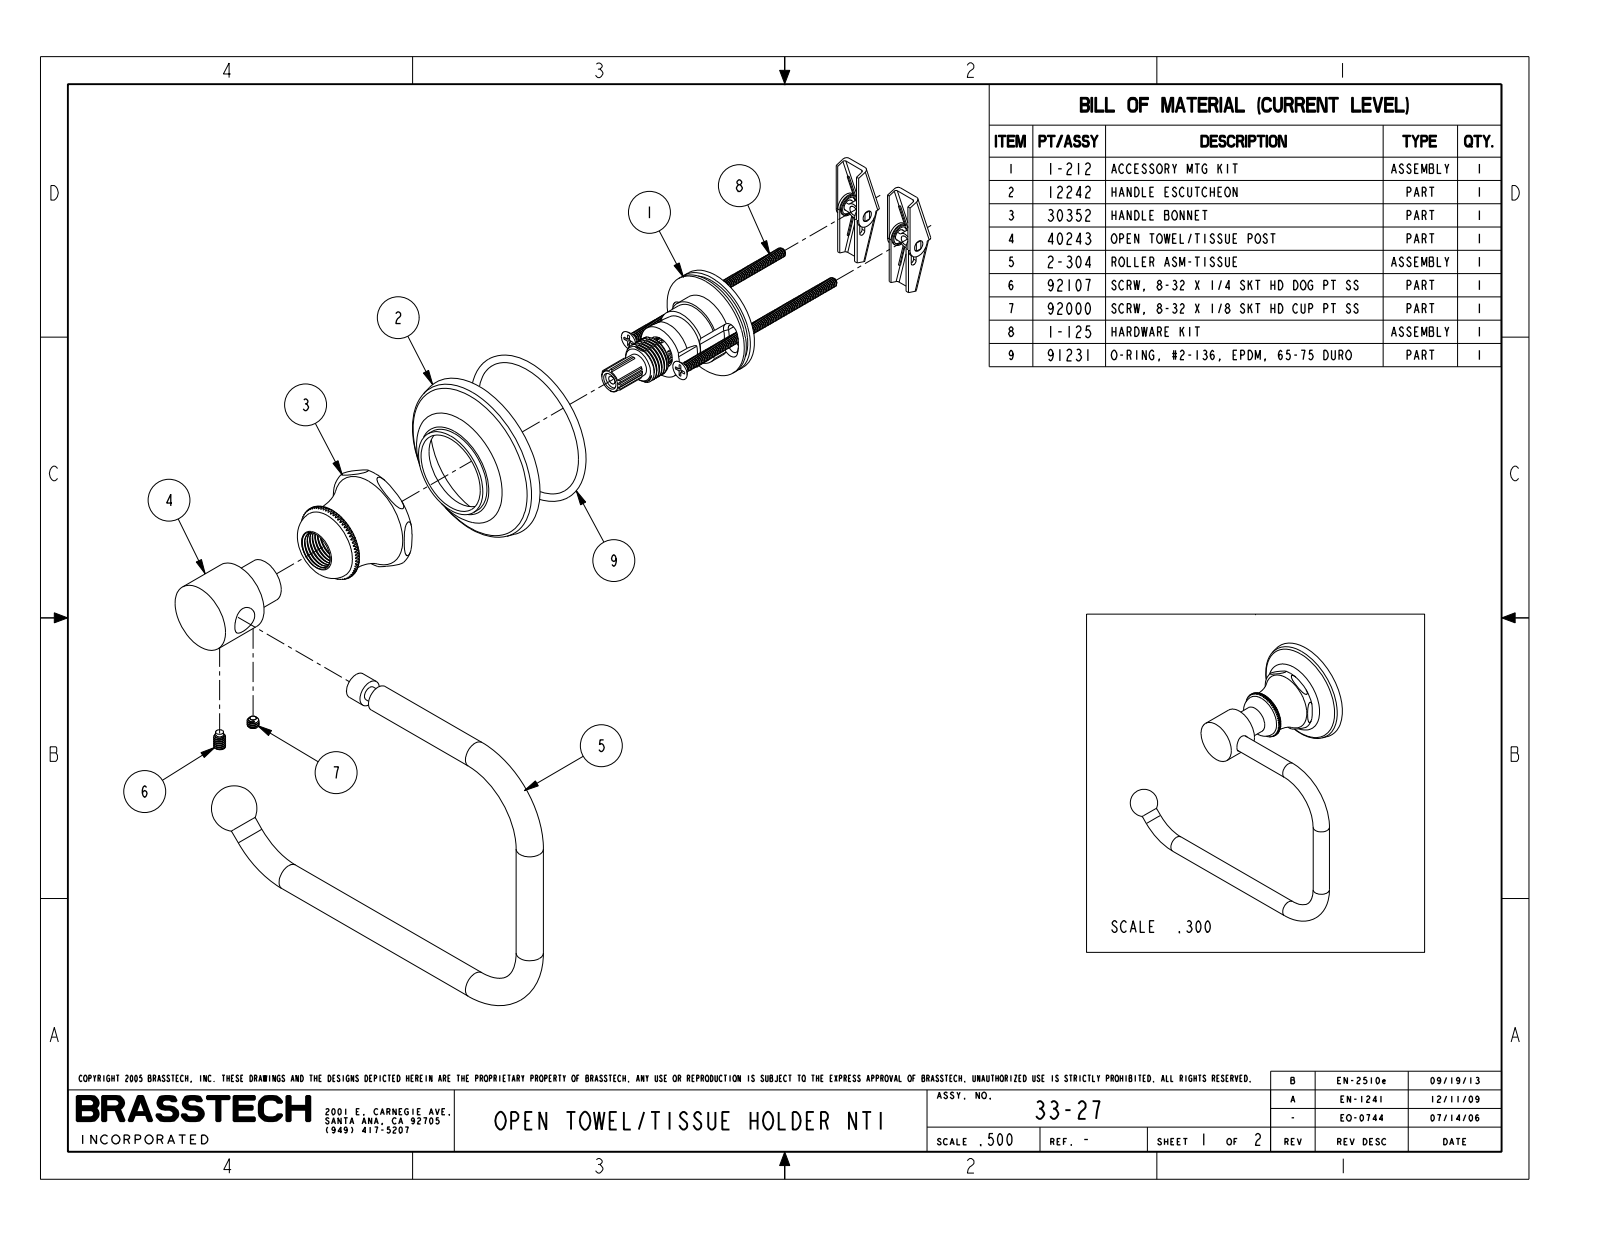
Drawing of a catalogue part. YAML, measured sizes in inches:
part_name: "33-27_WEB"
step_written_by: "PRO/ENGINEER BY PARAMETRIC TECHNOLOGY CORPORATION, 2009300 (CONFIG_CONTROL_DESIGN)"
units: inches
bodies: {solids: 0, faces: 103, planar: 57, cylindrical: 14, other: 32}
overall_size: [6.247, 5.245, 2.988]
round_bosses_or_shafts:
  - {diameter: 0.375, count: 4}
  - {diameter: 0.98, count: 1}
  - {diameter: 0.625, count: 1}
face_to_face_distances: [2.156, 1.38, 0.75, 4.014, 4.764, 1.017, 0.268]
